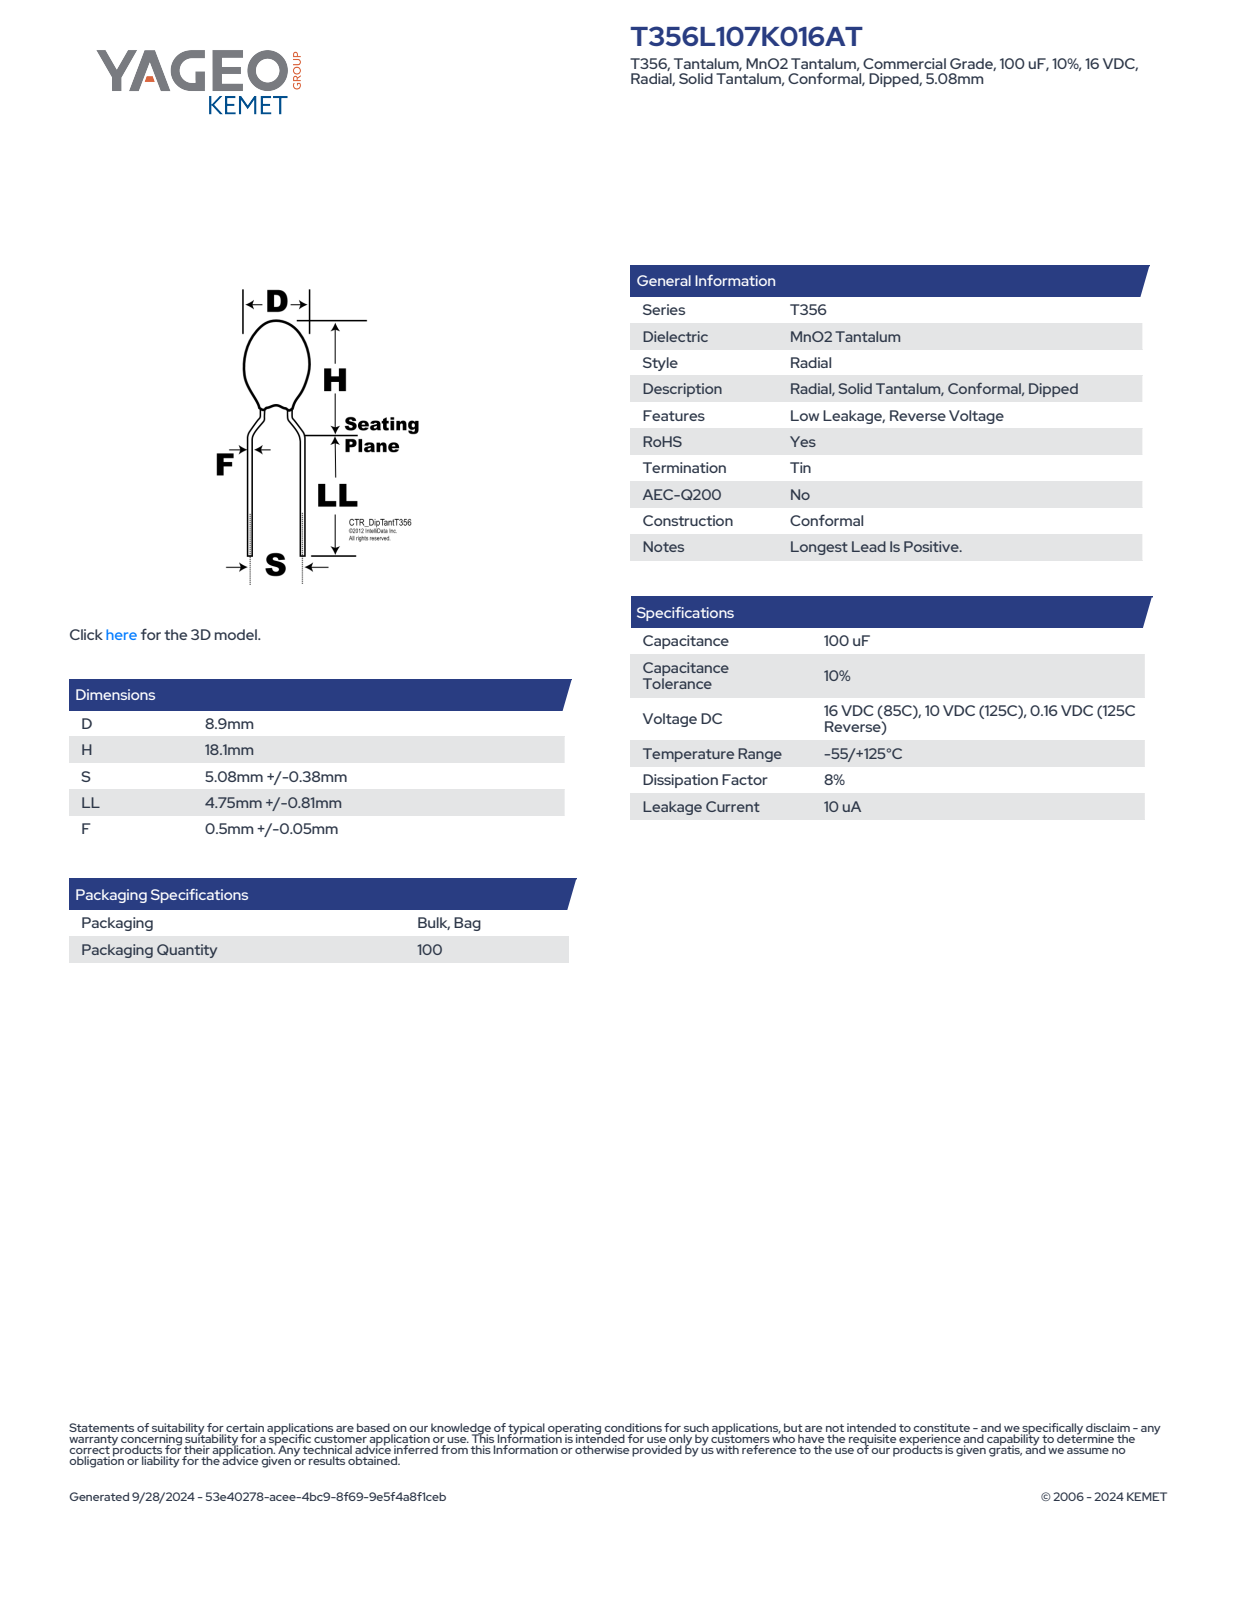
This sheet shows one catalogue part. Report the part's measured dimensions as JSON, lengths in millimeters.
{"part_name": "CTR_T356_D8.9H18.1S5.08LL5.56F0.55", "step_written_by": "SolidWorks 2014 (AUTOMOTIVE_DESIGN)", "units": "millimeters", "bodies": {"solids": 1, "faces": 96, "planar": 27, "cylindrical": 18, "other": 51}, "overall_size": [23.66, 8.9, 8.9], "volume_mm3": 680, "surface_area_mm2": 435, "round_bosses_or_shafts": [[0.55, 6], [8.9, 1]], "partial_cylinders_radius": [[4.44, 1]], "face_to_face_distances": [12.63, 11.03, 23.66, 19.16, 8.13, 4.5, 17.95, 6.92, 1.21, 5.71]}
